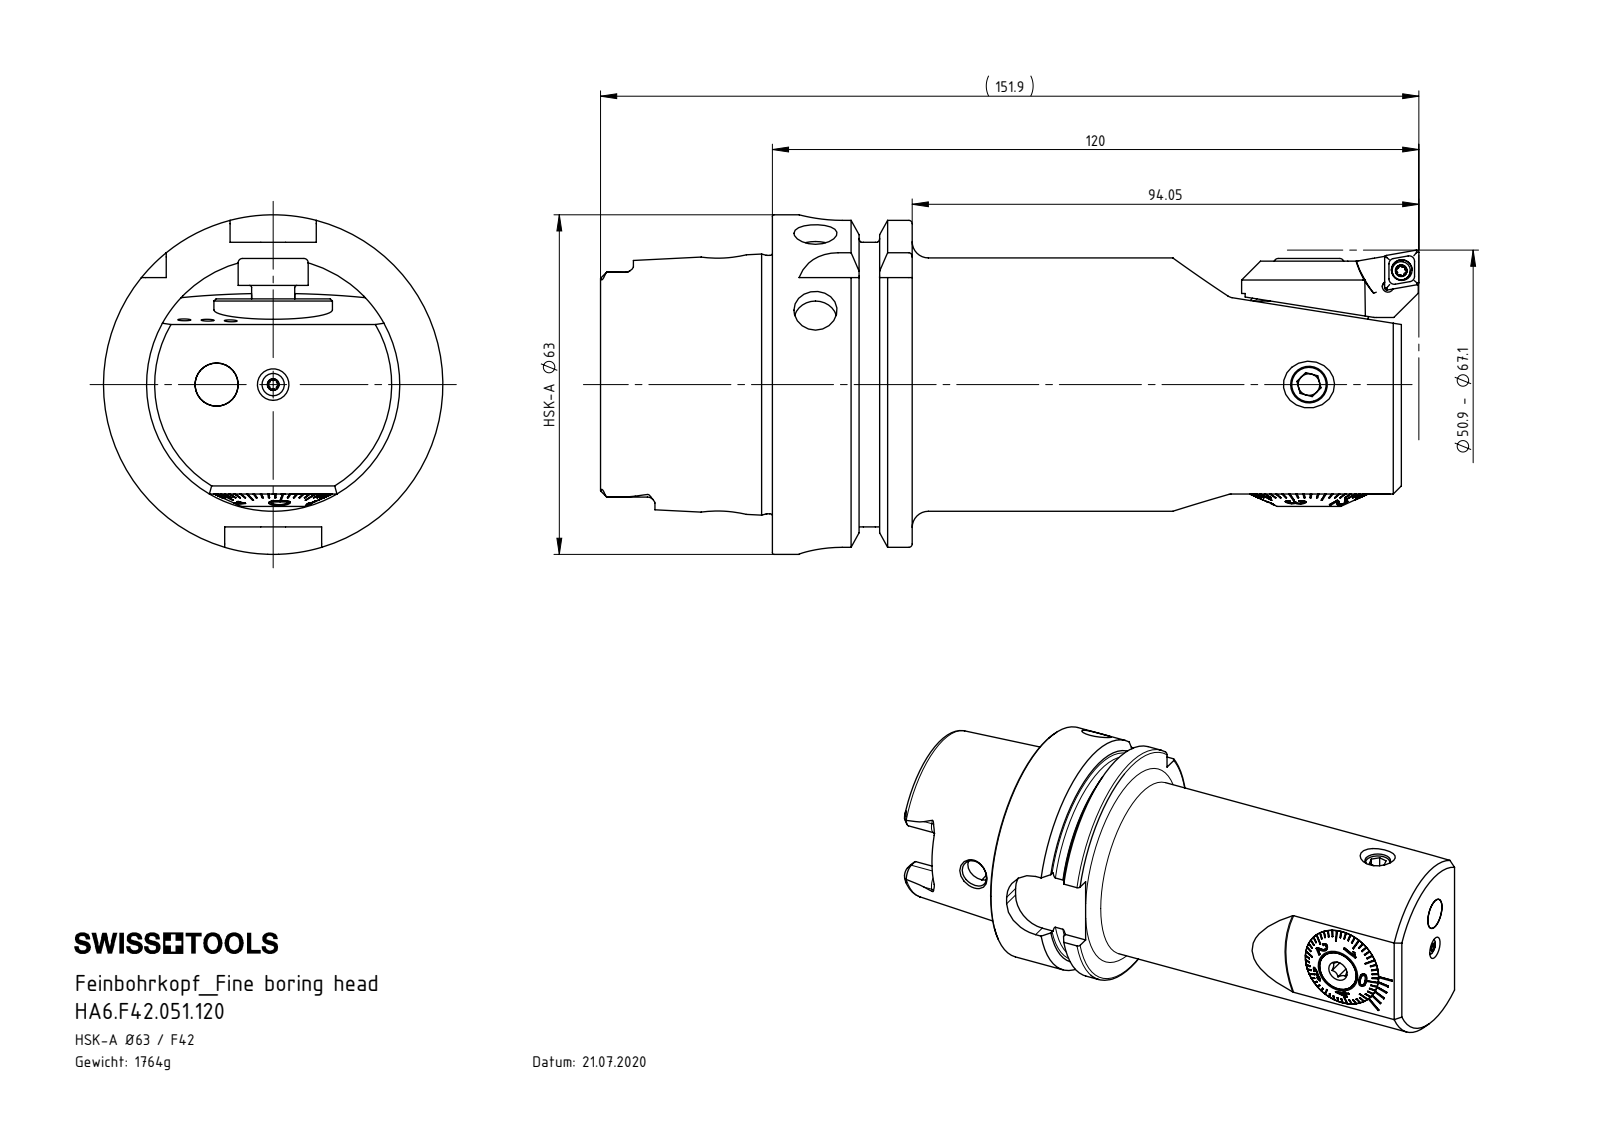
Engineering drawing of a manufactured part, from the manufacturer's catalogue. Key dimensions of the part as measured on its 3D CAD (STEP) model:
Part name (STEP PRODUCT): A42-BG2.011.014_C; F42-BG1.DA3.022_A; DIN 3771 - 19x1.5; HA6-F42.AA3.120_A_bohrungen gefllt (+8 more)
STEP written by: SolidWorks 2017 (AUTOMOTIVE_DESIGN)
Units: millimetres
Bodies: 13 solids, 660 faces (346 planar, 104 cylindrical, 210 other)
Overall size (bounding box): 148.65 × 63 × 63
Volume: 222 981 mm³ · Surface area: 49 957 mm²
Round holes (diameter × count): ⌀2.1 ×3, ⌀8 ×3, ⌀4.2 ×2, ⌀6.8 ×2, ⌀8.5 ×2, ⌀2.5 ×1, ⌀3 ×1, ⌀3.2 ×1, ⌀3.3 ×1, ⌀3.9 ×1, ⌀4 ×1, ⌀6 ×1
Round bosses / shafts (diameter × count): ⌀8 ×2, ⌀63 ×1, ⌀54.95 ×1, ⌀47.94 ×1, ⌀47 ×1, ⌀22 ×1, ⌀21.98 ×1, ⌀21.9 ×1
Partial cylindrical surfaces — rounded edges, fillets, slot ends (radius × count): R1.4 ×10, R0.21 ×6, R0.36 ×5, R2.88 ×4, R8 ×4, R0.5 ×3, R3.2 ×3, R2 ×2
Main face-to-face distances: 116.75, 25.95, 90.8, 16, 9.95, 106.8, 21.8, 5.6, 6.1, 7.2
Hole centre spacings: 10.5, 12.33, 92.6, 102.99, 108.6
